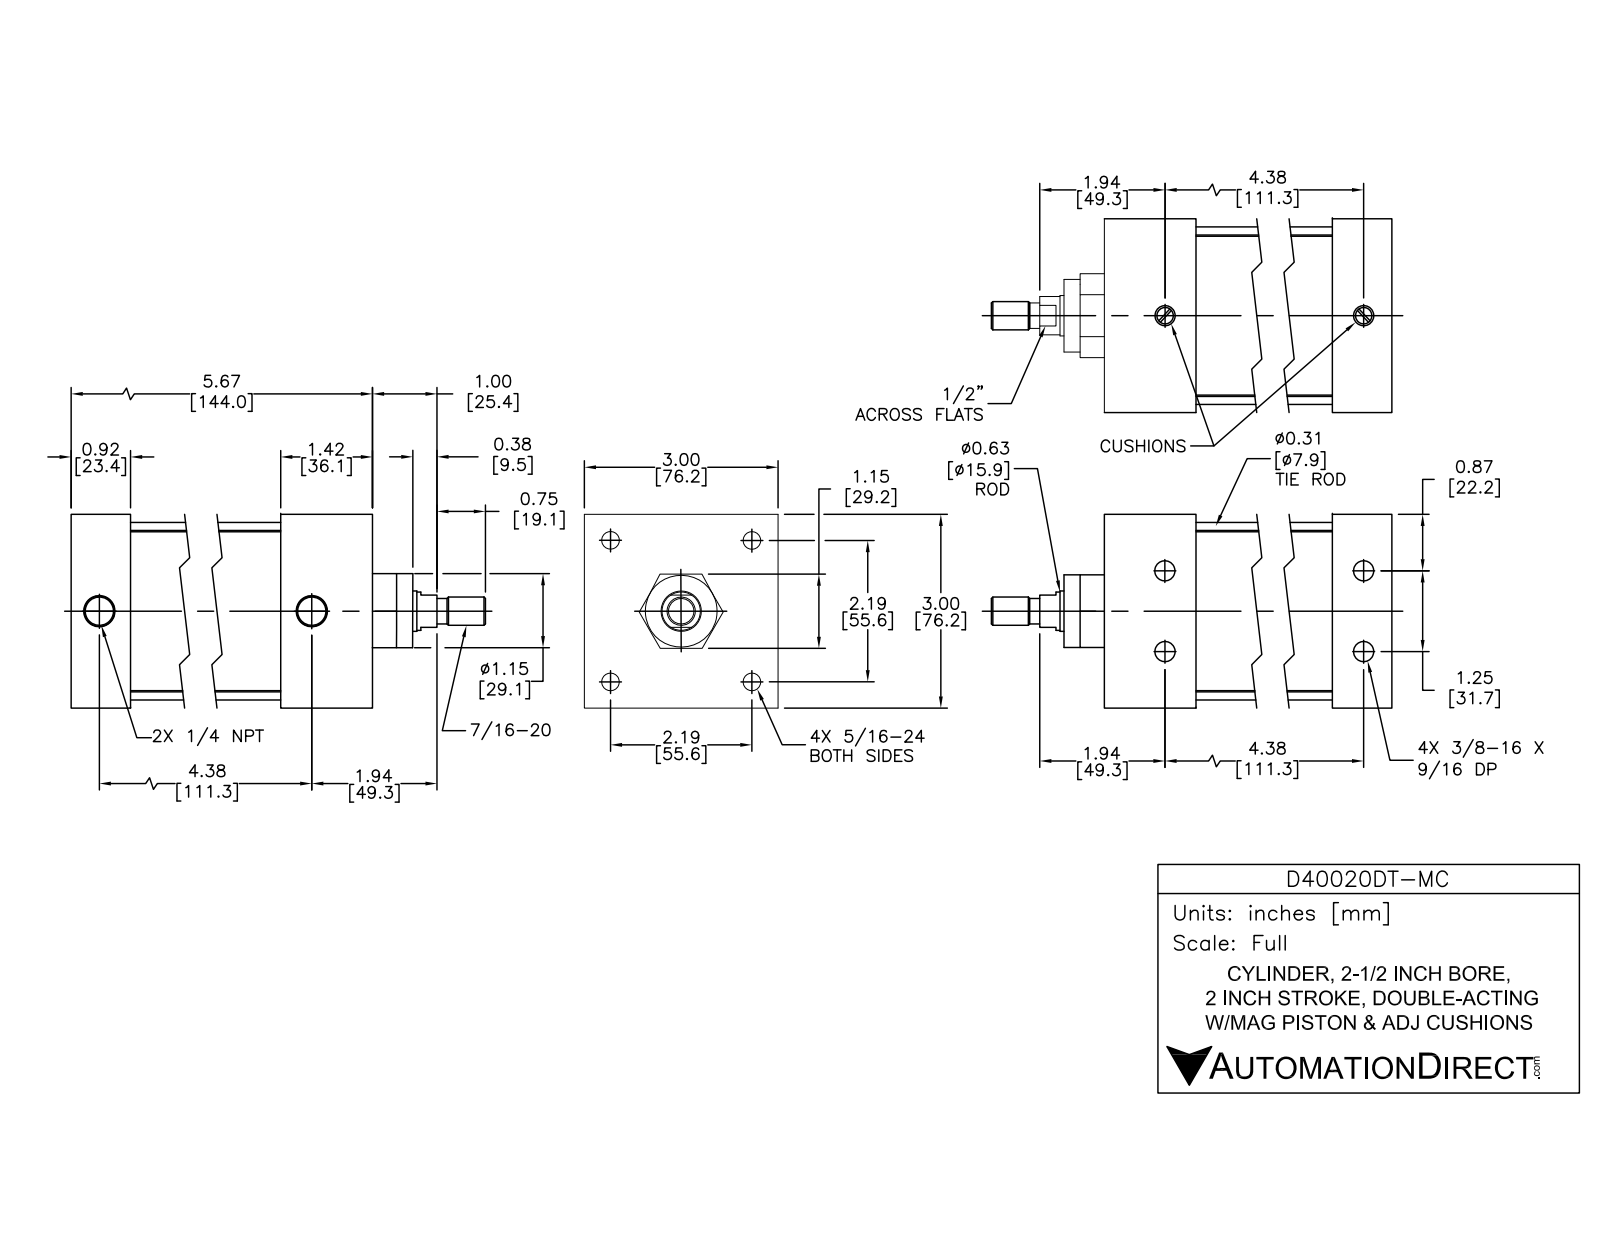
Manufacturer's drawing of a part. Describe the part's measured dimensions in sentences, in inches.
The part is named "D40020DT-MC; D40020DT-M PISTON; D40020DT-M BODY". Its 3-D file was written by "SolidWorks 2015 (AUTOMOTIVE_DESIGN)". It is 12 solids with 298 faces: 94 planar, 114 cylindrical and 90 other. Overall it measures 7.496 by 3 by 3 inches. Its volume is 32.38 cubic inches and its surface area 196.7 square inches. Round holes: 4 of diameter 0.267, 4 of diameter 0.307, 4 of diameter 0.359, 4 of diameter 0.5, 2 of diameter 0.297, 2 of diameter 0.477, 1 of diameter 0.625, 1 of diameter 0.628, 1 of diameter 2.5. Round bosses or shafts: 4 of diameter 0.484, 4 of diameter 0.313, 4 of diameter 0.282, 1 of diameter 2.75, 1 of diameter 2.497, 1 of diameter 1.12, 1 of diameter 0.622, 1 of diameter 0.59. Partial cylindrical surfaces (rounded edges, fillets, slot ends): 4 of radius 0.3. The main face-to-face distances are 3, 0.08, 3.326, 5.746, 4.726, 1.02, 1.42, 3.306, 4.326, 1. The hole center spacings are 1.556, 2.2, 4.414, 4.37, 0.625, 0.625, 1.25, 3.111.
